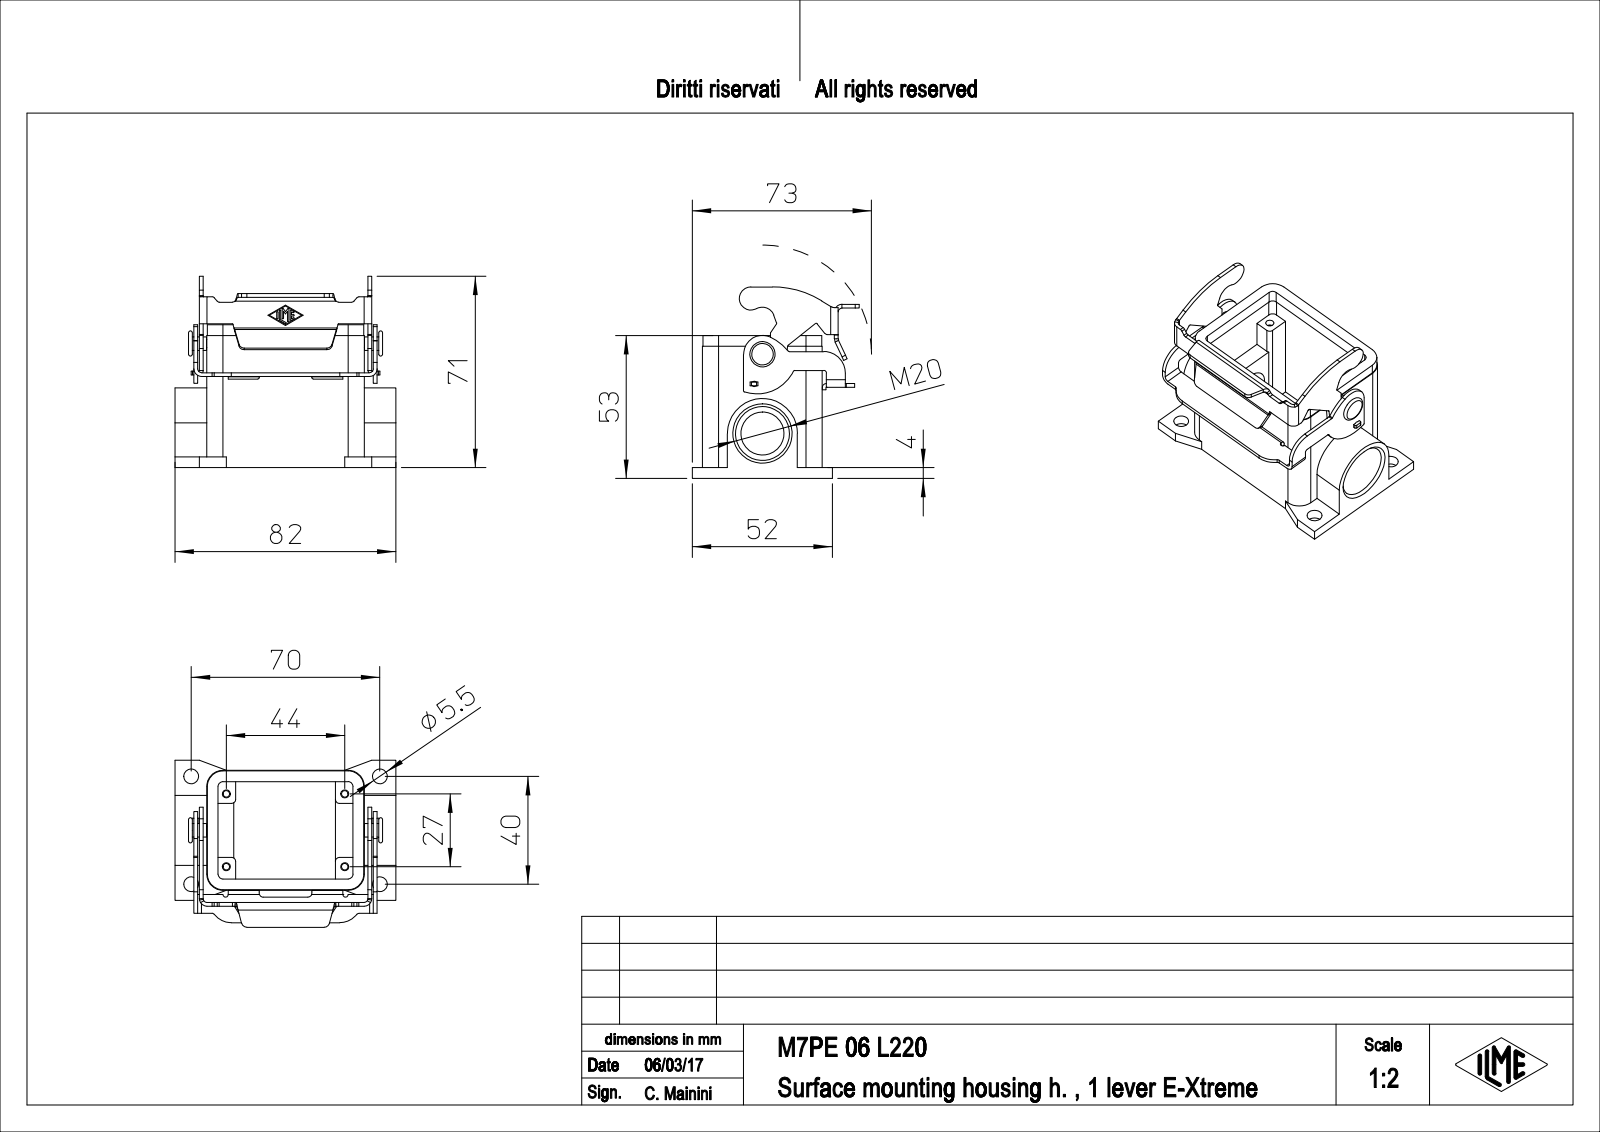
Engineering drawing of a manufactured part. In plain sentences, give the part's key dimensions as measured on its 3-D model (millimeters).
The part is named "M7PE_06_L220". Its 3-D file was written by "PTC Creo Elements/Direct Modeling 19.0E 27-Jun-2016 (C) Parametric Technology GmbH (AUTOMOTIVE_DESIGN)". It is 1 solid with 386 faces: 198 planar, 168 cylindrical and 20 other. Overall it measures 82 by 71 by 61.98 millimeters. Its volume is 73 378 cubic millimeters and its surface area 38 703 square millimeters. Round holes: 4 of diameter 2.46, 4 of diameter 3, 4 of diameter 5.5, 1 of diameter 16, 1 of diameter 20. Round bosses or shafts: 1 of diameter 5, 1 of diameter 3. Partial cylindrical surfaces (rounded edges, fillets, slot ends): 16 of radius 0.25, 13 of radius 1, 12 of radius 0.5, 11 of radius 1.5, 8 of radius 2, 6 of radius 1.4, 6 of radius 2.8, 4 of radius 1.8. The main face-to-face distances are 4, 1.4, 40.5, 44.5, 2, 64.6, 6.75, 36.5, 50.5, 10.75. The hole center spacings are 14.53, 35.93, 57.37, 66.12, 27, 40, 44, 51.62.
